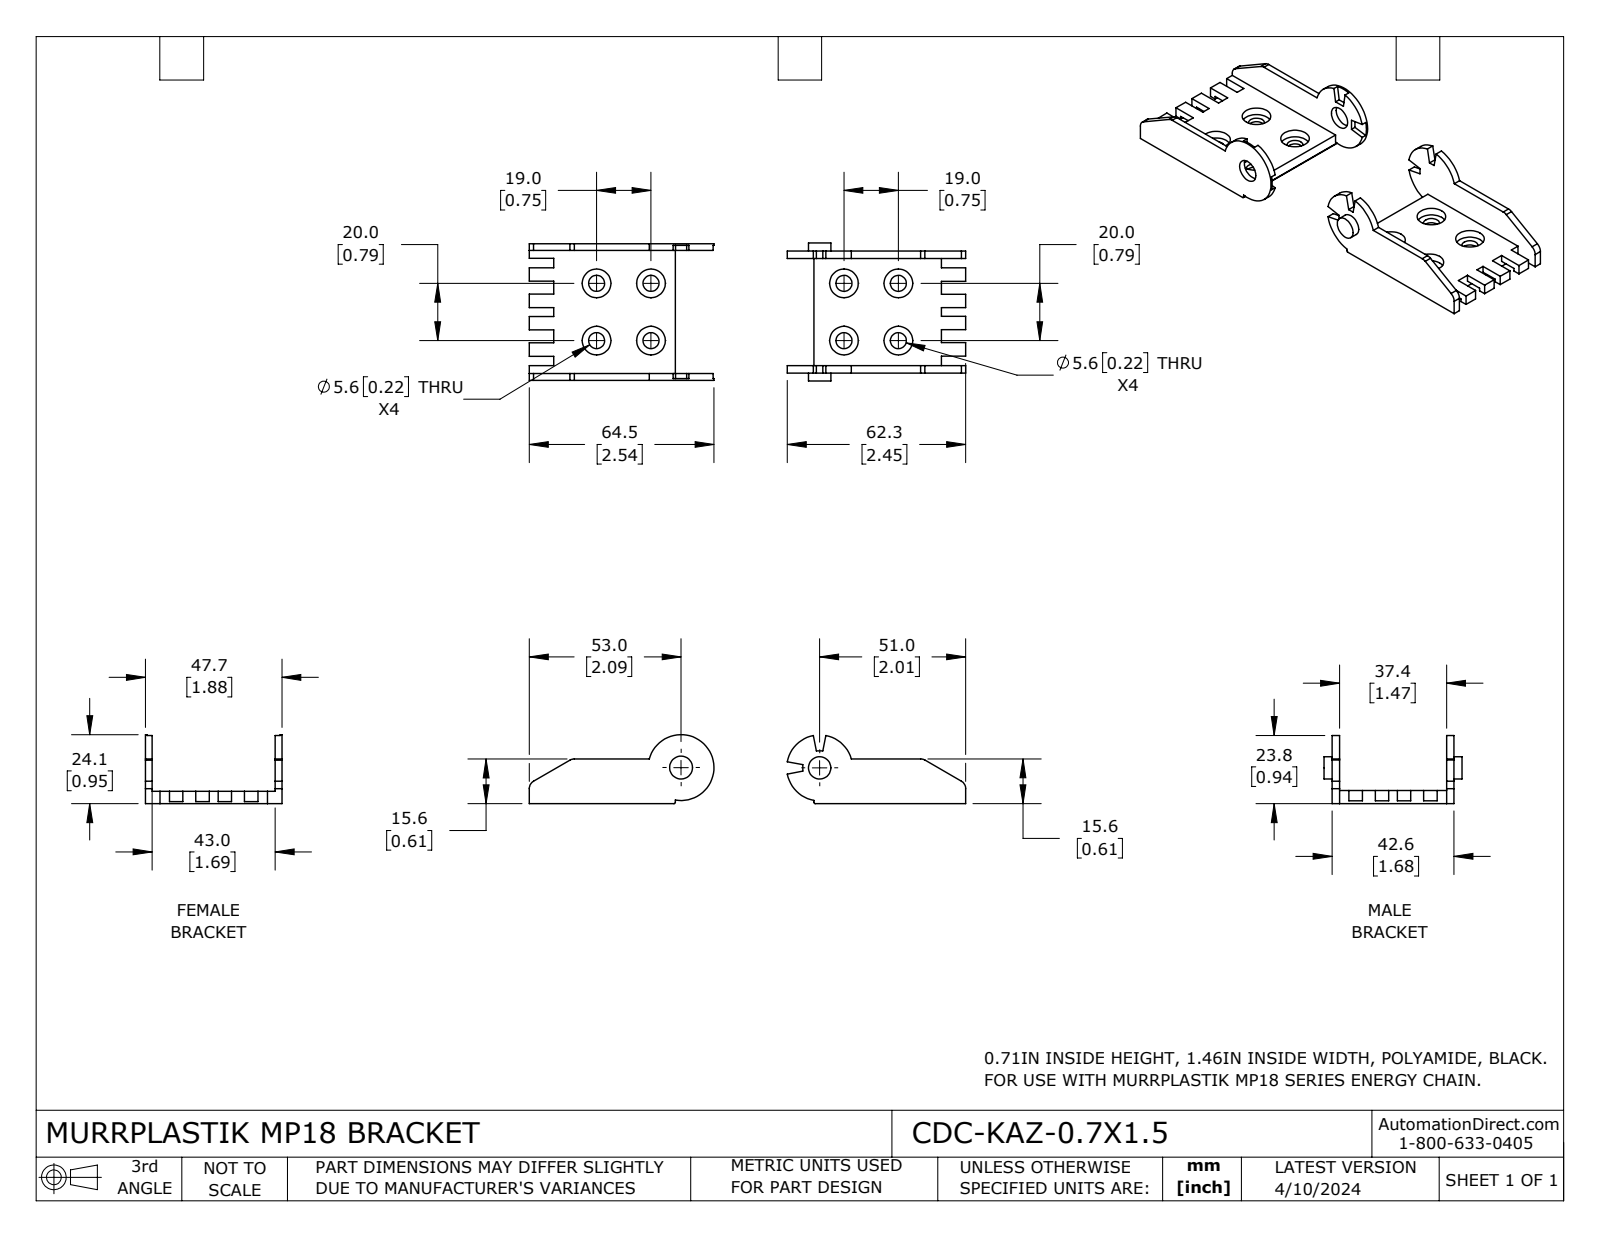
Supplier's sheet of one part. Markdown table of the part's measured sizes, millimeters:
| quantity | value |
| --- | --- |
| part name | CDC-KAZ-0.7X1.5; CDC-KAZ-0.7X1.5_Female; CDC-KAZ-0.7X1.5_Male |
| STEP written by | SolidWorks 2023 (CONFIG_CONTROL_DESIGN) |
| units | millimeters |
| bodies | 2 solids, 176 faces (116 planar, 60 cylindrical, 0 other) |
| overall size | 152.4 × 48.2 × 24.1 |
| volume | 24 320 mm³ |
| surface area | 18 420 mm² |
| round holes (diameter × count) | 5.6 × 8, 10 × 8, 8 × 1 |
| round bosses / shafts (diameter × count) | 7.8 × 1 |
| partial cylindrical surfaces (radius × count) | 3 × 4, 0.5 × 2, 11.5 × 2 |
| main face-to-face distances | 2.8, 2.5, 45.2, 4.3, 2.6, 5.2, 42.5, 40, 42.8, 4.6 |
| hole center spacings | 19, 20, 27.6, 86.4, 88.7, 67.4, 70.3, 105.4 |
